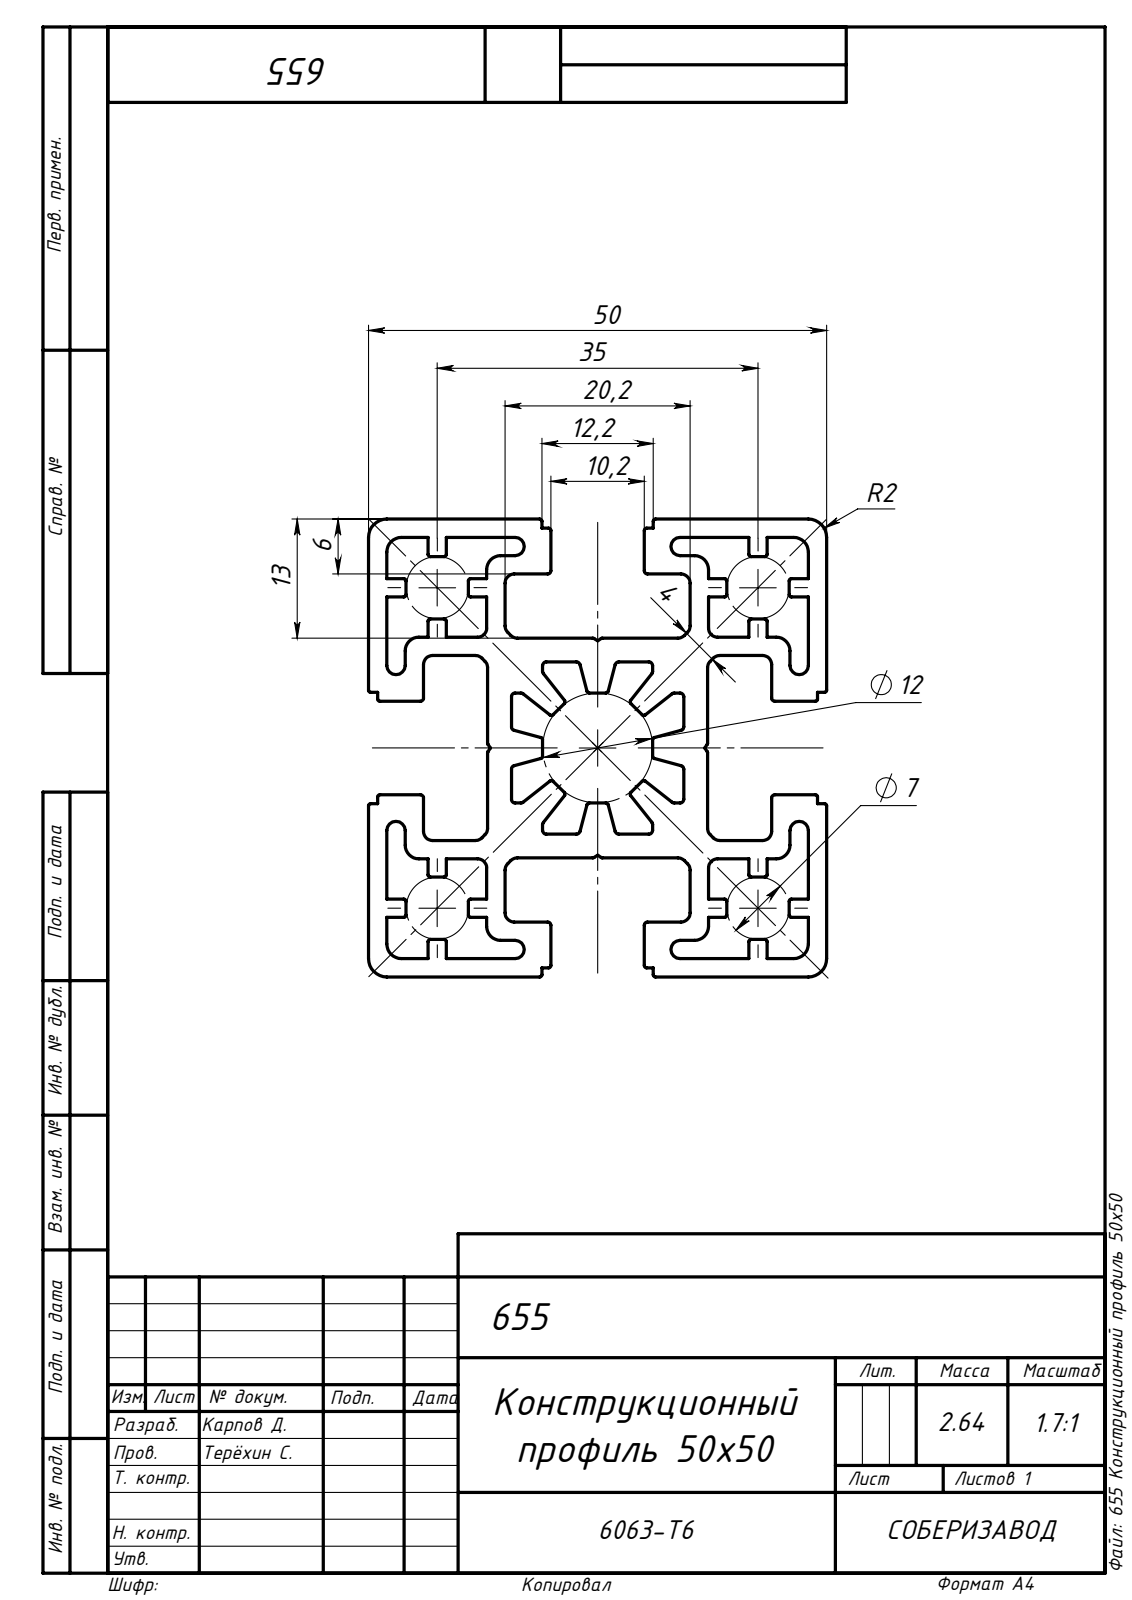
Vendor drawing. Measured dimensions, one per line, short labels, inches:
name: 655 Конструкционный профиль 50х50
written by: SolidWorks 2019 (AUTOMOTIVE_DESIGN)
unit: in
bodies: 1 solid, 374 faces (202 planar, 172 cylindrical, 0 other)
size: 39.37 × 1.969 × 1.969
volume: 59.72 in³; area: 1 200 in²
rounds: 72× R0.01, 36× R0.039, 24× R0.016, 8× R0.014, 8× R0.059, 4× R0.063, 4× R0.079
face distances: 0.079, 1.378, 0.256, 1.89, 1.457, 0.508, 1.382, 1.969, 0.512, 0.433
